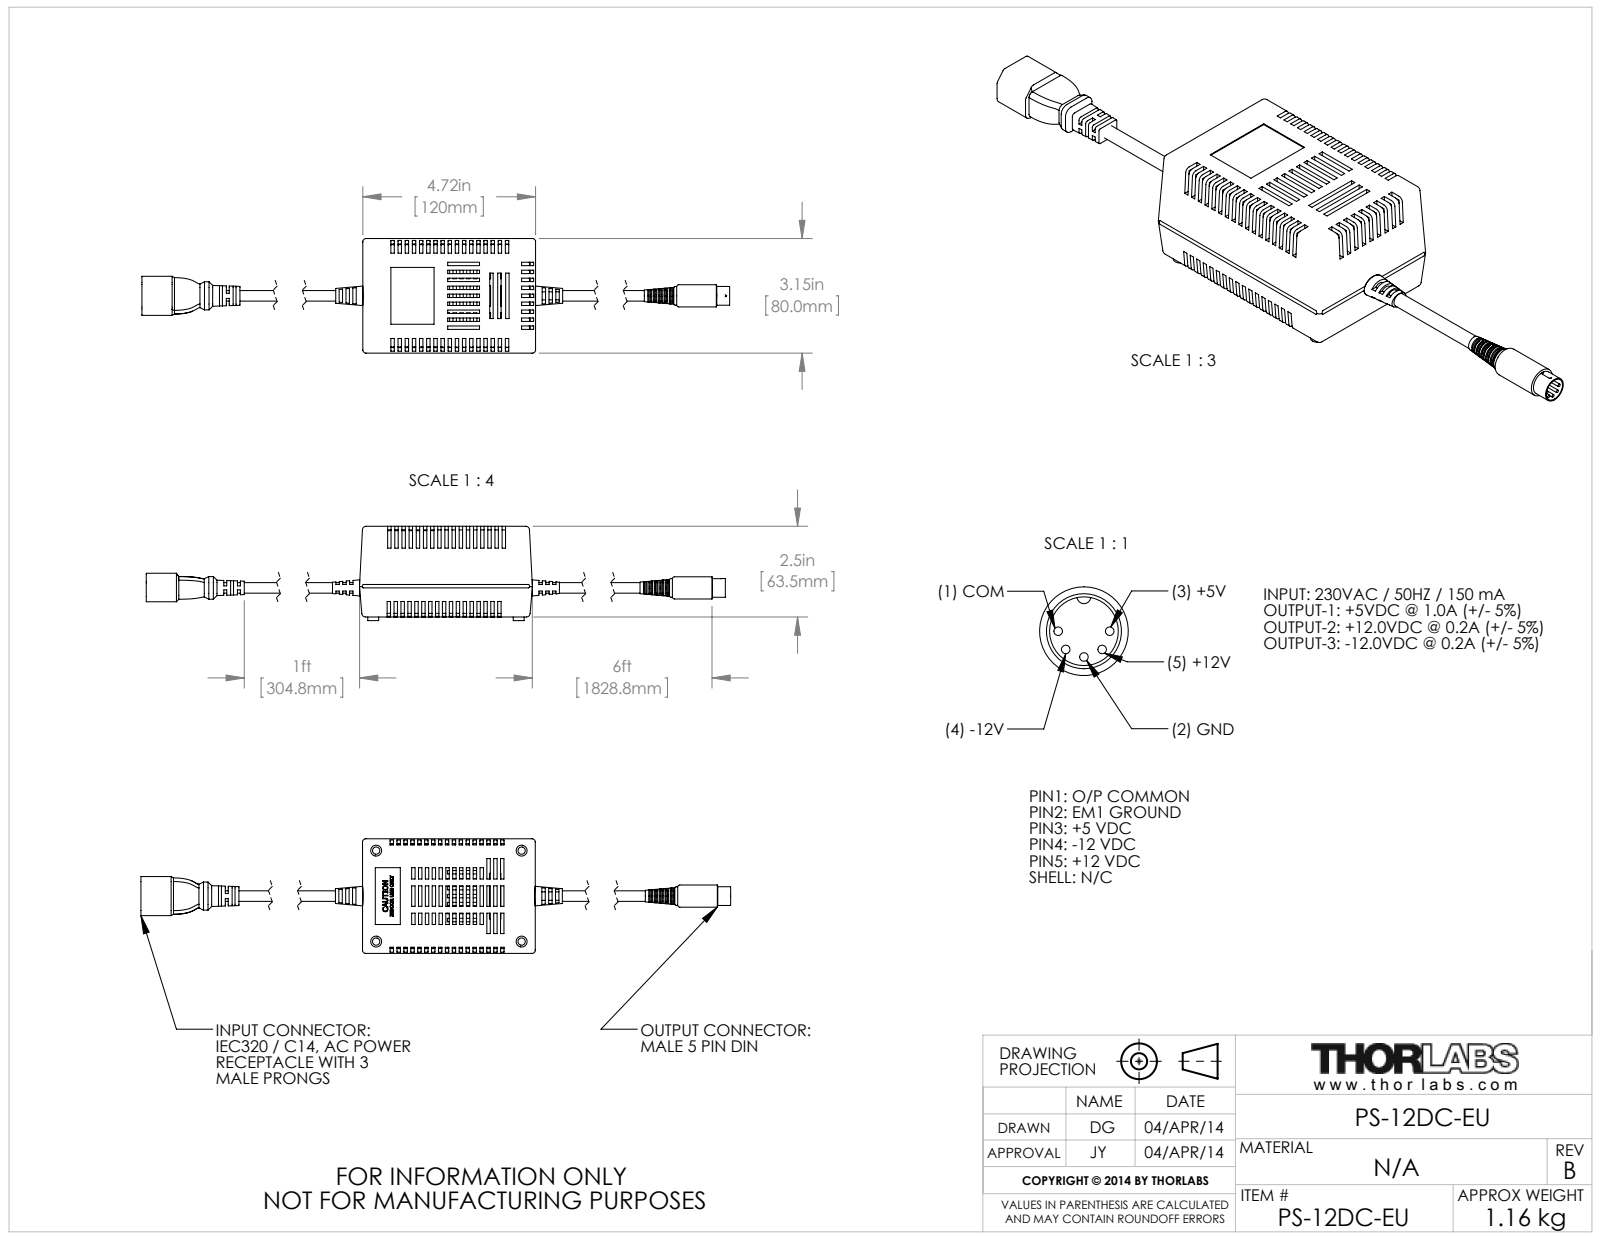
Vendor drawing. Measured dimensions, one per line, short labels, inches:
name: PS-12DC-EU-E0W; SD-50; PS-12DC-US-EU; User Library-IEC 320 C14
written by: SolidWorks 2012 (AUTOMOTIVE_DESIGN)
unit: in
bodies: 4 solids, 1410 faces (1074 planar, 165 cylindrical, 171 other)
size: 15.72 × 3.15 × 2.594
volume: 7.346 in³; area: 155.9 in²
holes: 4× ⌀0.2, 1× ⌀0.25, 1× ⌀0.253, 1× ⌀0.472
bosses: 5× ⌀0.059, 4× ⌀0.3, 1× ⌀0.61, 1× ⌀0.516, 1× ⌀0.512, 1× ⌀0.29
rounds: 20× R0.1, 4× R0.072, 4× R0.161, 2× R0.02, 2× R0.028, 2× R0.062, 2× R0.142, 1× R0.047
face distances: 0.1, 2.394, 2.494, 2.294, 0.02, 2.374, 0.08, 2.474, 0.12, 2.274
hole spacings: 2.5, 4, 4.717
